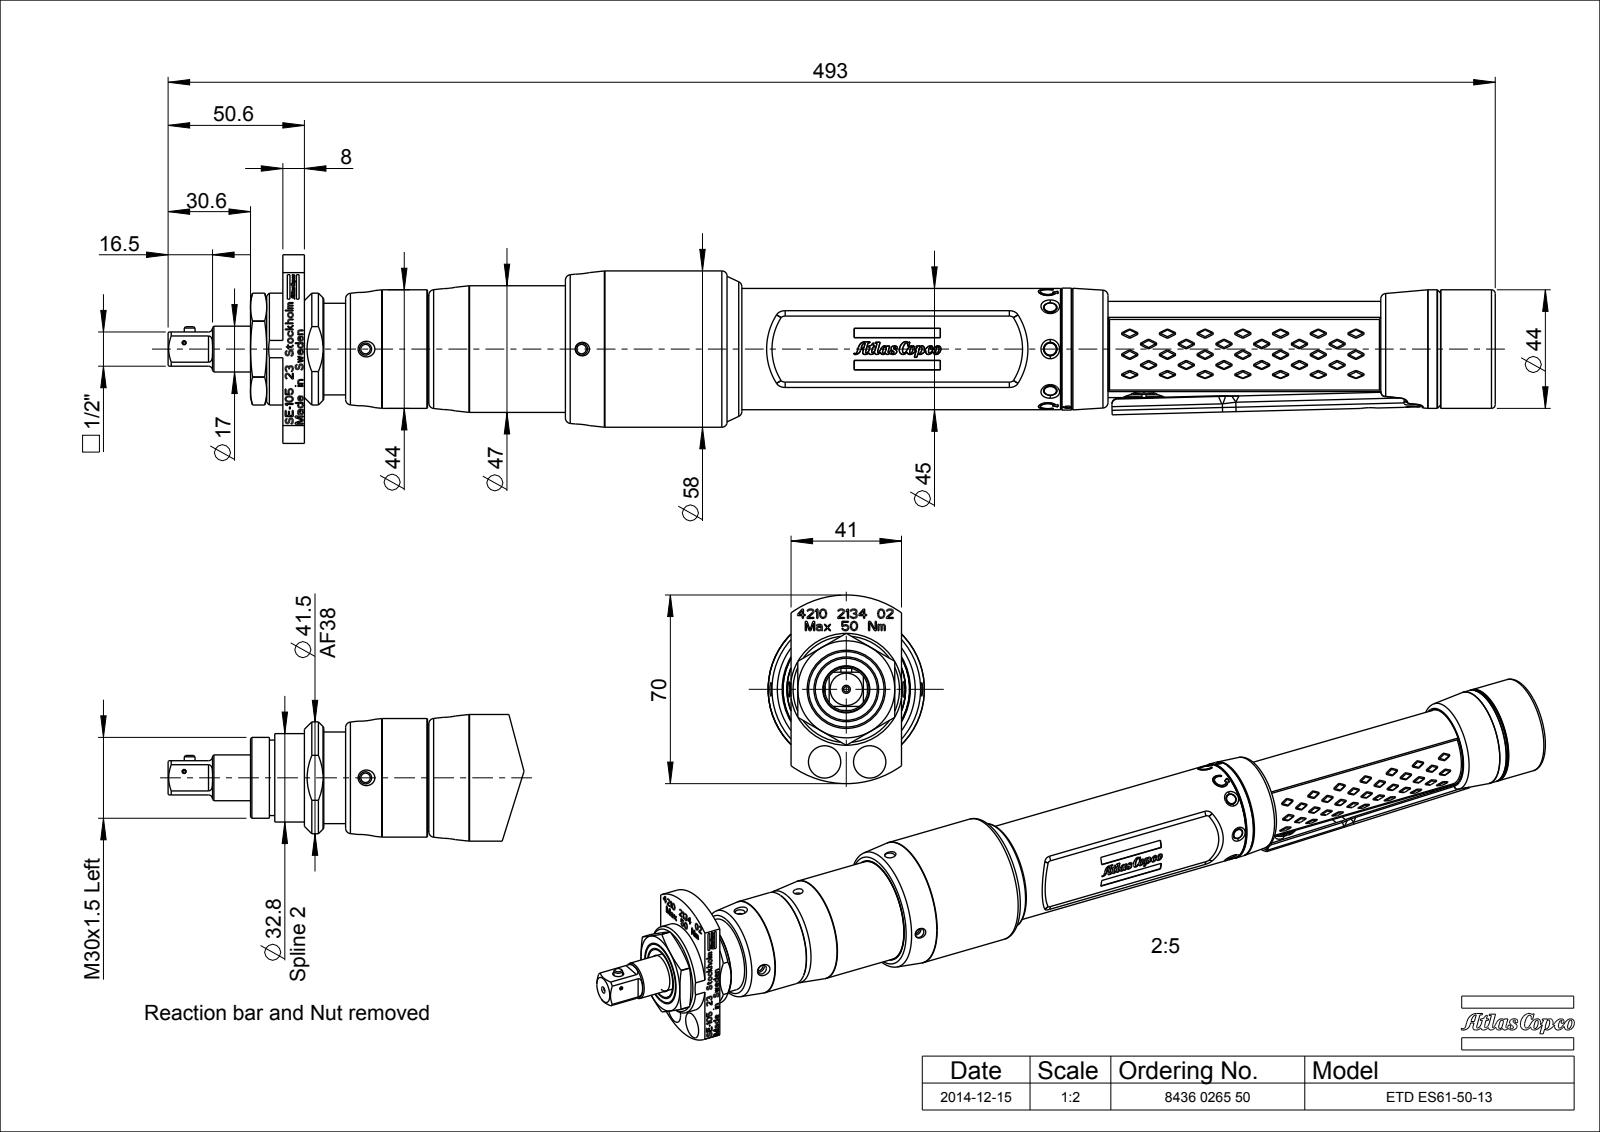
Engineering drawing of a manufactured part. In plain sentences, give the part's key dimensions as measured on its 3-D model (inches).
The part is named "4220388170_AF0; 4220388112_AF0; 4220388172_AF0_ASM; 4220388180_ASM (+8 more)". Its 3-D file was written by "PRO/ENGINEER BY PARAMETRIC TECHNOLOGY CORPORATION, 2013410 (CONFIG_CONTROL_DESIGN)". It is 44 solids with 5242 faces: 2051 planar, 916 cylindrical and 2275 other. Overall it measures 19.398 by 2.756 by 2.283 inches. Its volume is 21.76 cubic inches and its surface area 433.1 square inches. Round holes: 12 of diameter 0.104, 12 of diameter 0.129, 12 of diameter 0.142, 6 of diameter 0.177, 5 of diameter 0.098, 5 of diameter 0.165, 5 of diameter 0.197, 1 of diameter 0.035, 1 of diameter 0.059, 1 of diameter 0.079, 1 of diameter 0.102, 1 of diameter 0.11. Round bosses or shafts: 9 of diameter 0.087, 9 of diameter 0.075, 9 of diameter 0.062, 7 of diameter 0.126, 3 of diameter 0.115, 2 of diameter 0.472, 2 of diameter 0.12, 2 of diameter 0.1. Partial cylindrical surfaces (rounded edges, fillets, slot ends): 60 of radius 0.008, 26 of radius 0.016, 24 of radius 0.079, 18 of radius 0.039, 14 of radius 0.02, 12 of radius 0.004, 10 of radius 0.01, 8 of radius 0.059. The main face-to-face distances are 0.236, 0.315, 0.118, 0.039, 0.059, 0.551, 0.472, 16.799, 0.787, 1.634. The hole center spacings are 0.244, 0.374, 0.578, 0.773, 0.934, 0.231, 0.529, 0.571.
